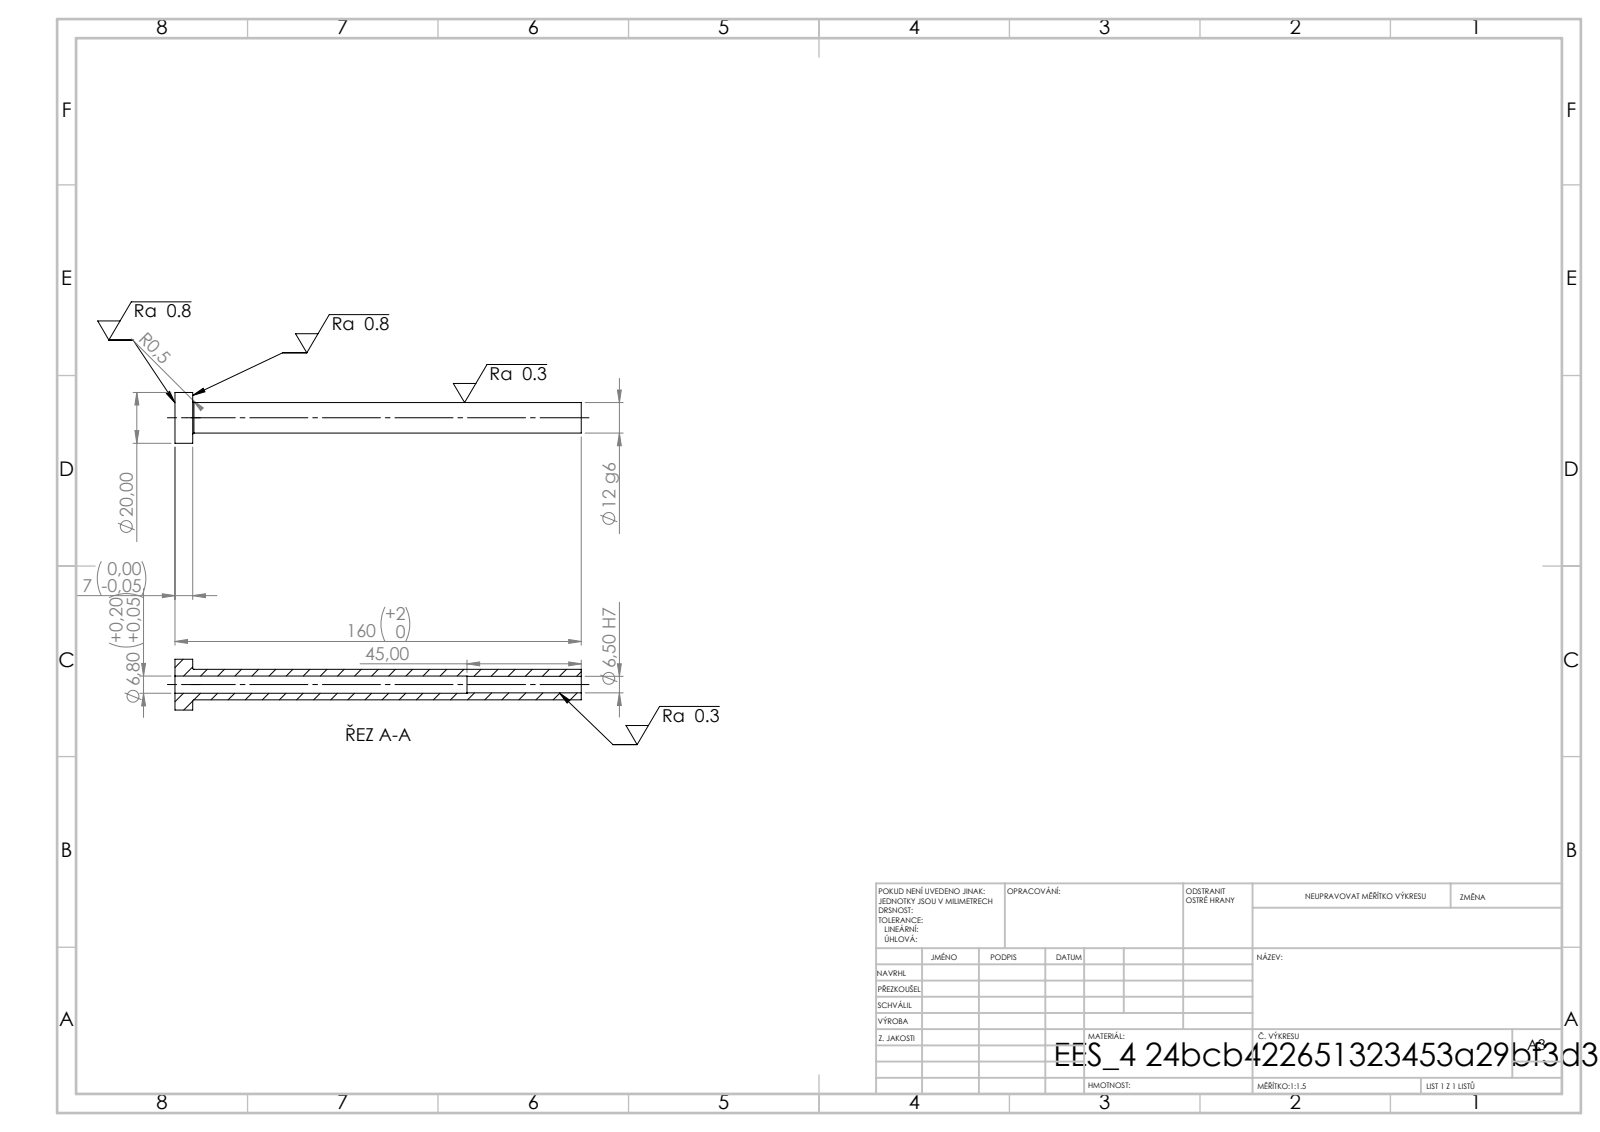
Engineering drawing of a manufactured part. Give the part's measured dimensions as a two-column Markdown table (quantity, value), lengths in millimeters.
| quantity | value |
| --- | --- |
| STEP written by | SolidWorks 2019 (CONFIG_CONTROL_DESIGN) |
| units | millimeters |
| bodies | 1 solid, 14 faces (4 planar, 8 cylindrical, 2 other) |
| overall size | 160 × 20 × 20 |
| volume | 13 835 mm³ |
| surface area | 10 137 mm² |
| round holes (diameter × count) | 6.5 × 1, 6.8 × 1 |
| round bosses / shafts (diameter × count) | 20 × 1, 12 × 1 |
| main face-to-face distances | 7, 160, 153, 115, 108, 45 |
